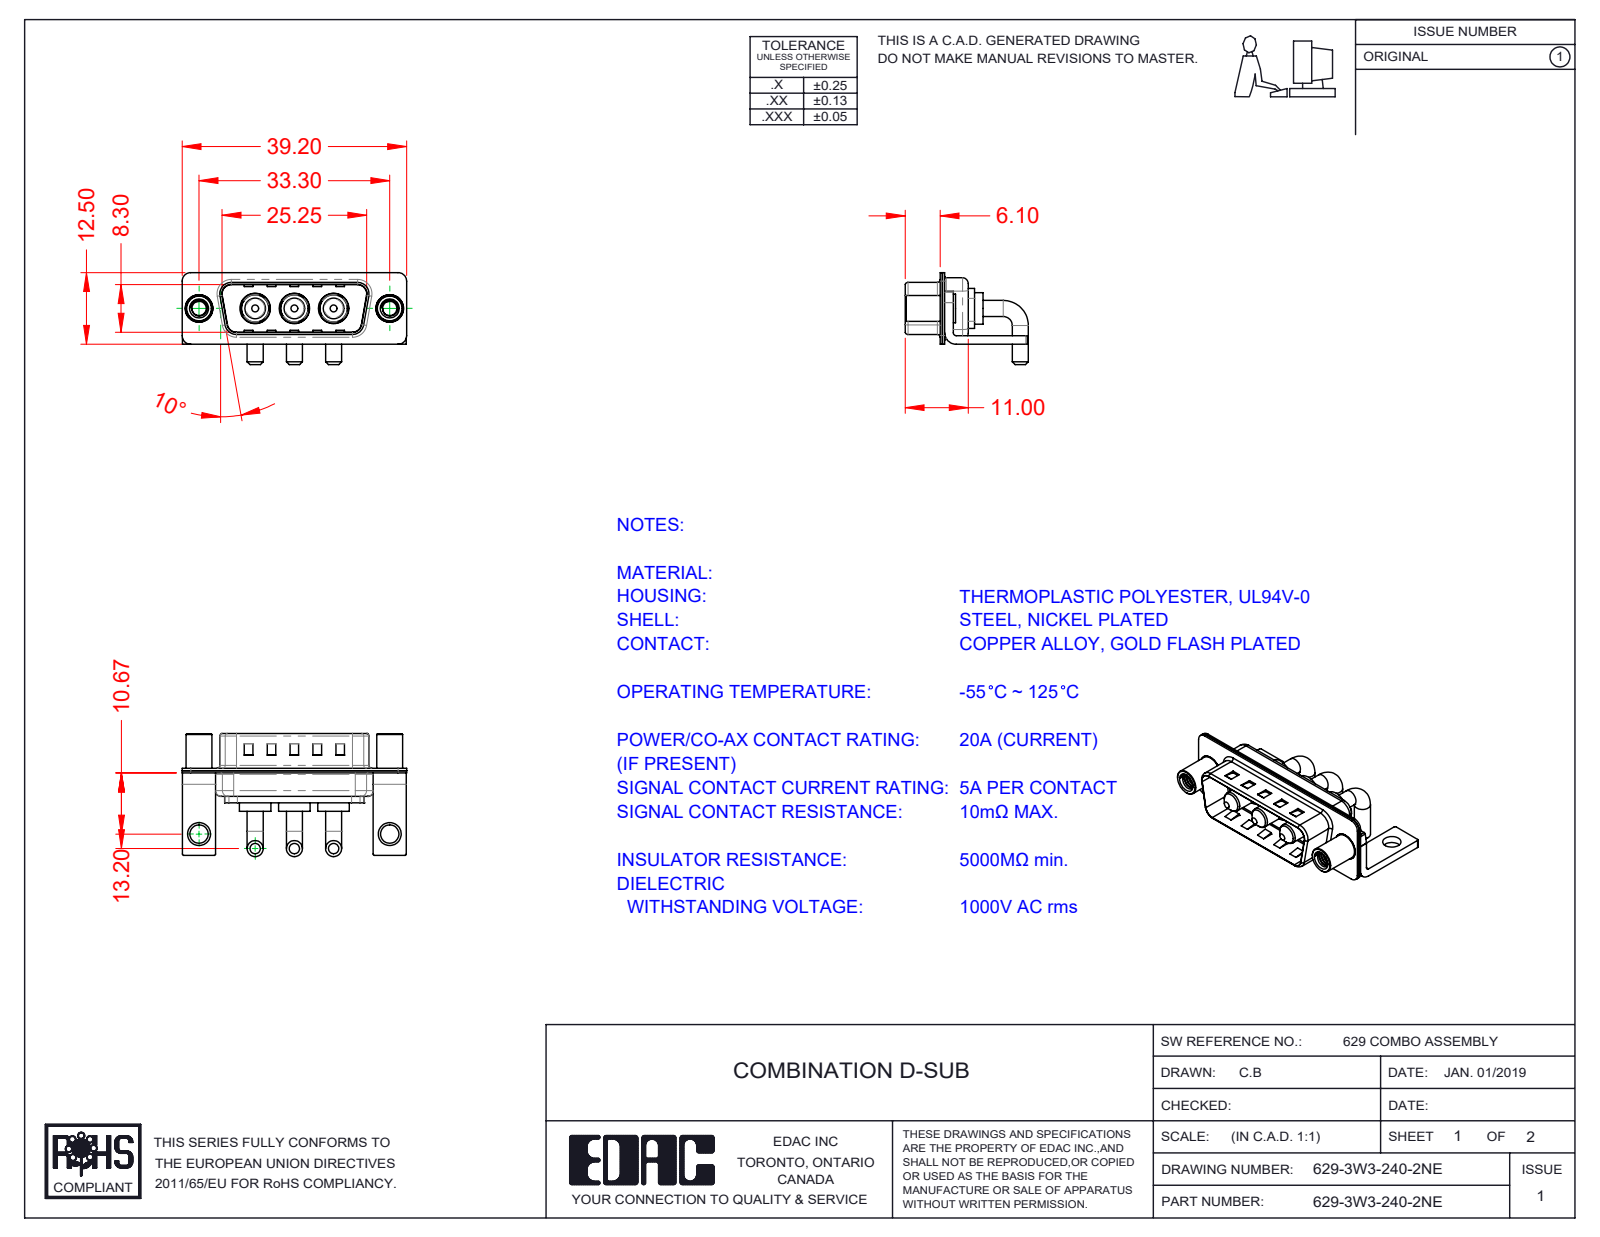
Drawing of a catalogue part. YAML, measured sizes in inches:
part_name: "629Combo Stabilizer Bracket; 629Combo Shell Rear_15 Contacts; 629-3W3-240-2NE; Power Pin_20A RA (+3 more)"
step_written_by: "SolidWorks 2020 (CONFIG_CONTROL_DESIGN)"
units: inches
bodies: {solids: 13, faces: 567, planar: 191, cylindrical: 268, other: 108}
overall_size: [1.543, 0.846, 0.632]
volume: 0.161
surface_area: 9.167
round_holes:
  - {diameter: 0.191, count: 3}
  - {diameter: 0.209, count: 3}
  - {diameter: 0.098, count: 2}
  - {diameter: 0.126, count: 2}
  - {diameter: 0.157, count: 2}
  - {diameter: 0.189, count: 2}
round_bosses_or_shafts:
  - {diameter: 0.11, count: 6}
  - {diameter: 0.217, count: 3}
  - {diameter: 0.205, count: 3}
  - {diameter: 0.187, count: 3}
  - {diameter: 0.148, count: 3}
  - {diameter: 0.142, count: 3}
  - {diameter: 0.197, count: 2}
  - {diameter: 0.193, count: 2}
partial_cylinders:
  - {radius: 0.01, count: 16}
  - {radius: 0.059, count: 16}
  - {radius: 0.079, count: 13}
  - {radius: 0.02, count: 9}
  - {radius: 0.063, count: 8}
  - {radius: 0.024, count: 4}
  - {radius: 0.026, count: 4}
  - {radius: 0.035, count: 4}
face_to_face_distances: [0.016, 0.031, 0.059, 0.374, 0.358, 0.343, 0.39, 0.205, 0.03, 0.024]
hole_center_spacings: [0.27, 0.386, 0.656, 0.925, 1.311, 0.539]
